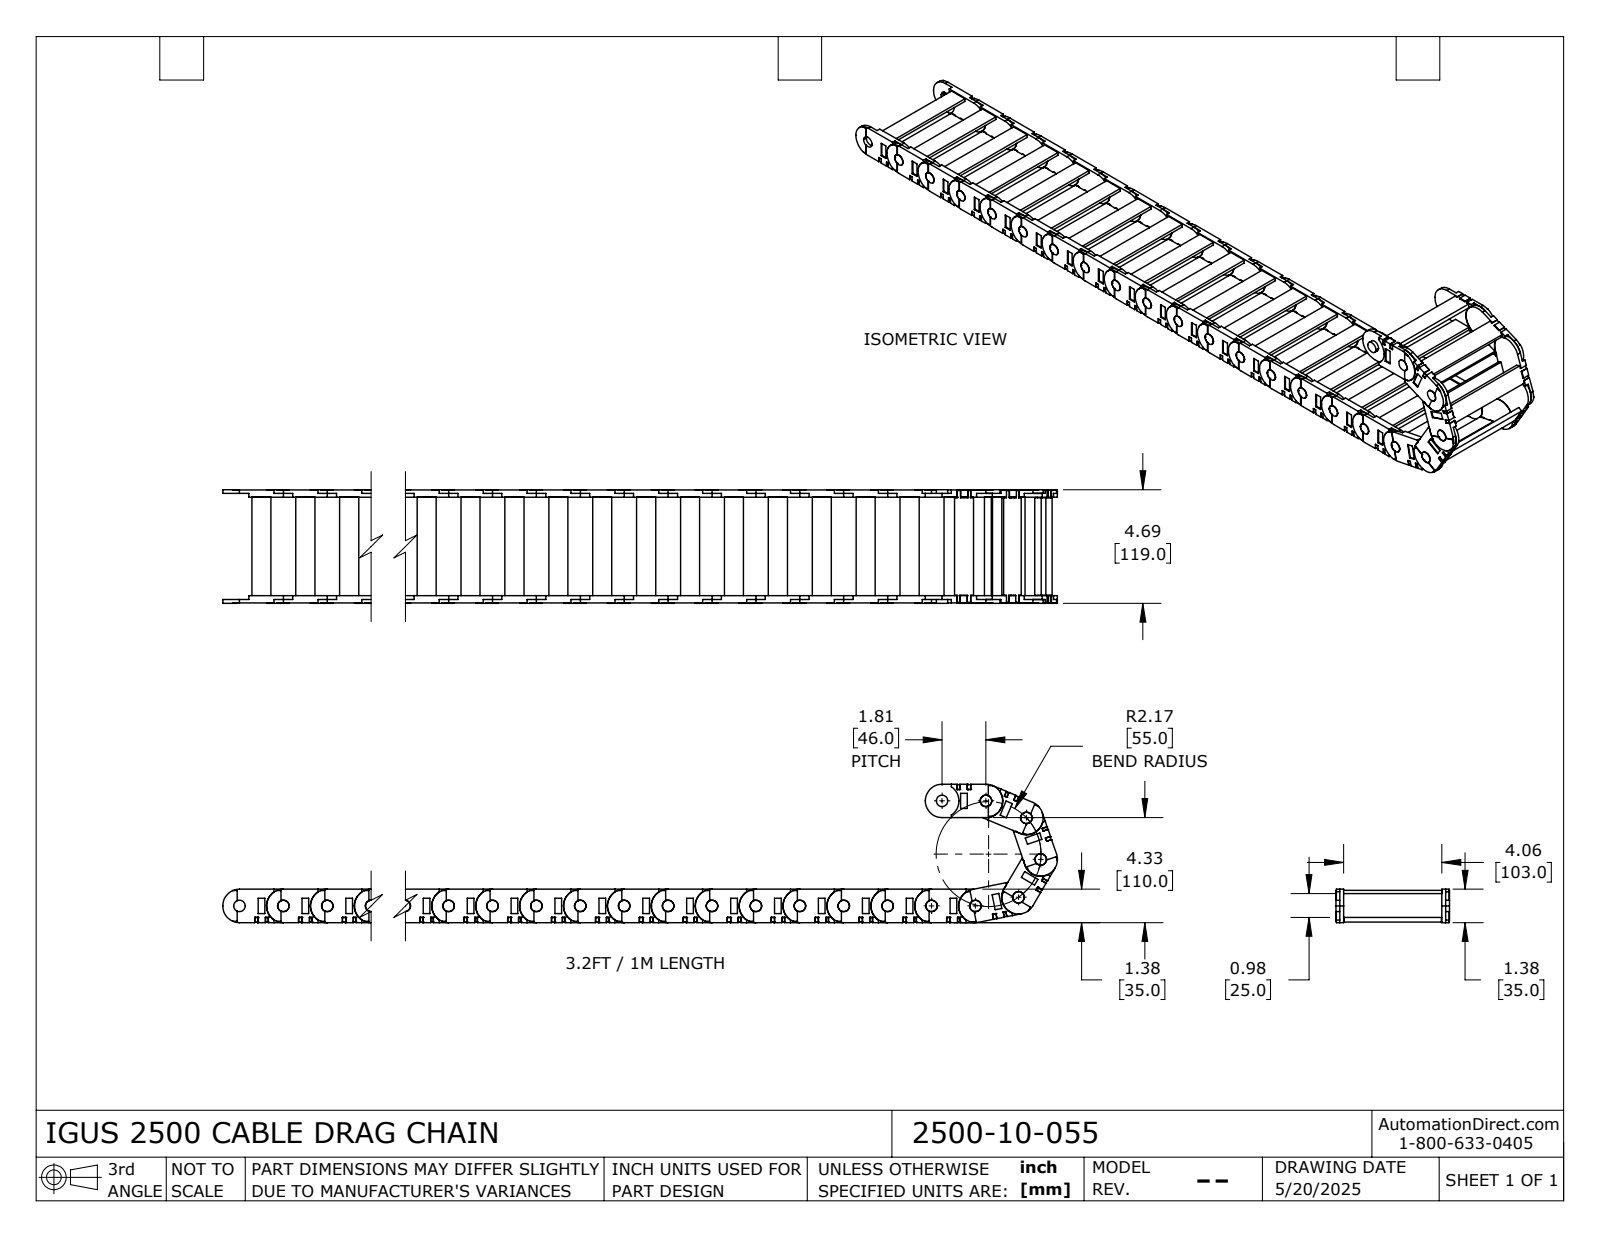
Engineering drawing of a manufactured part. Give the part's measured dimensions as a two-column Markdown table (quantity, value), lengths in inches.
| quantity | value |
| --- | --- |
| part name | 2500_10_055 |
| STEP written by | SolidWorks 2024 (AUTOMOTIVE_DESIGN) |
| units | inches |
| bodies | 66 solids, 2398 faces (1870 planar, 528 cylindrical, 0 other) |
| overall size | 34.858 × 5.709 × 4.685 |
| volume | 55.55 in³ |
| surface area | 815.8 in² |
| round holes (diameter × count) | 0.473 × 22 |
| round bosses / shafts (diameter × count) | 0.472 × 22, 1.378 × 21 |
| partial cylindrical surfaces (radius × count) | 0.697 × 23, 0.689 × 2 |
| main face-to-face distances | 0.157, 4.213, 4.37, 4.354, 0.134, 0.197, 0.142, 0.299, 4.512, 0.984 |
| hole center spacings | 1.811, 3.622, 5.433, 7.244, 9.055, 10.866, 12.677, 14.488 |
